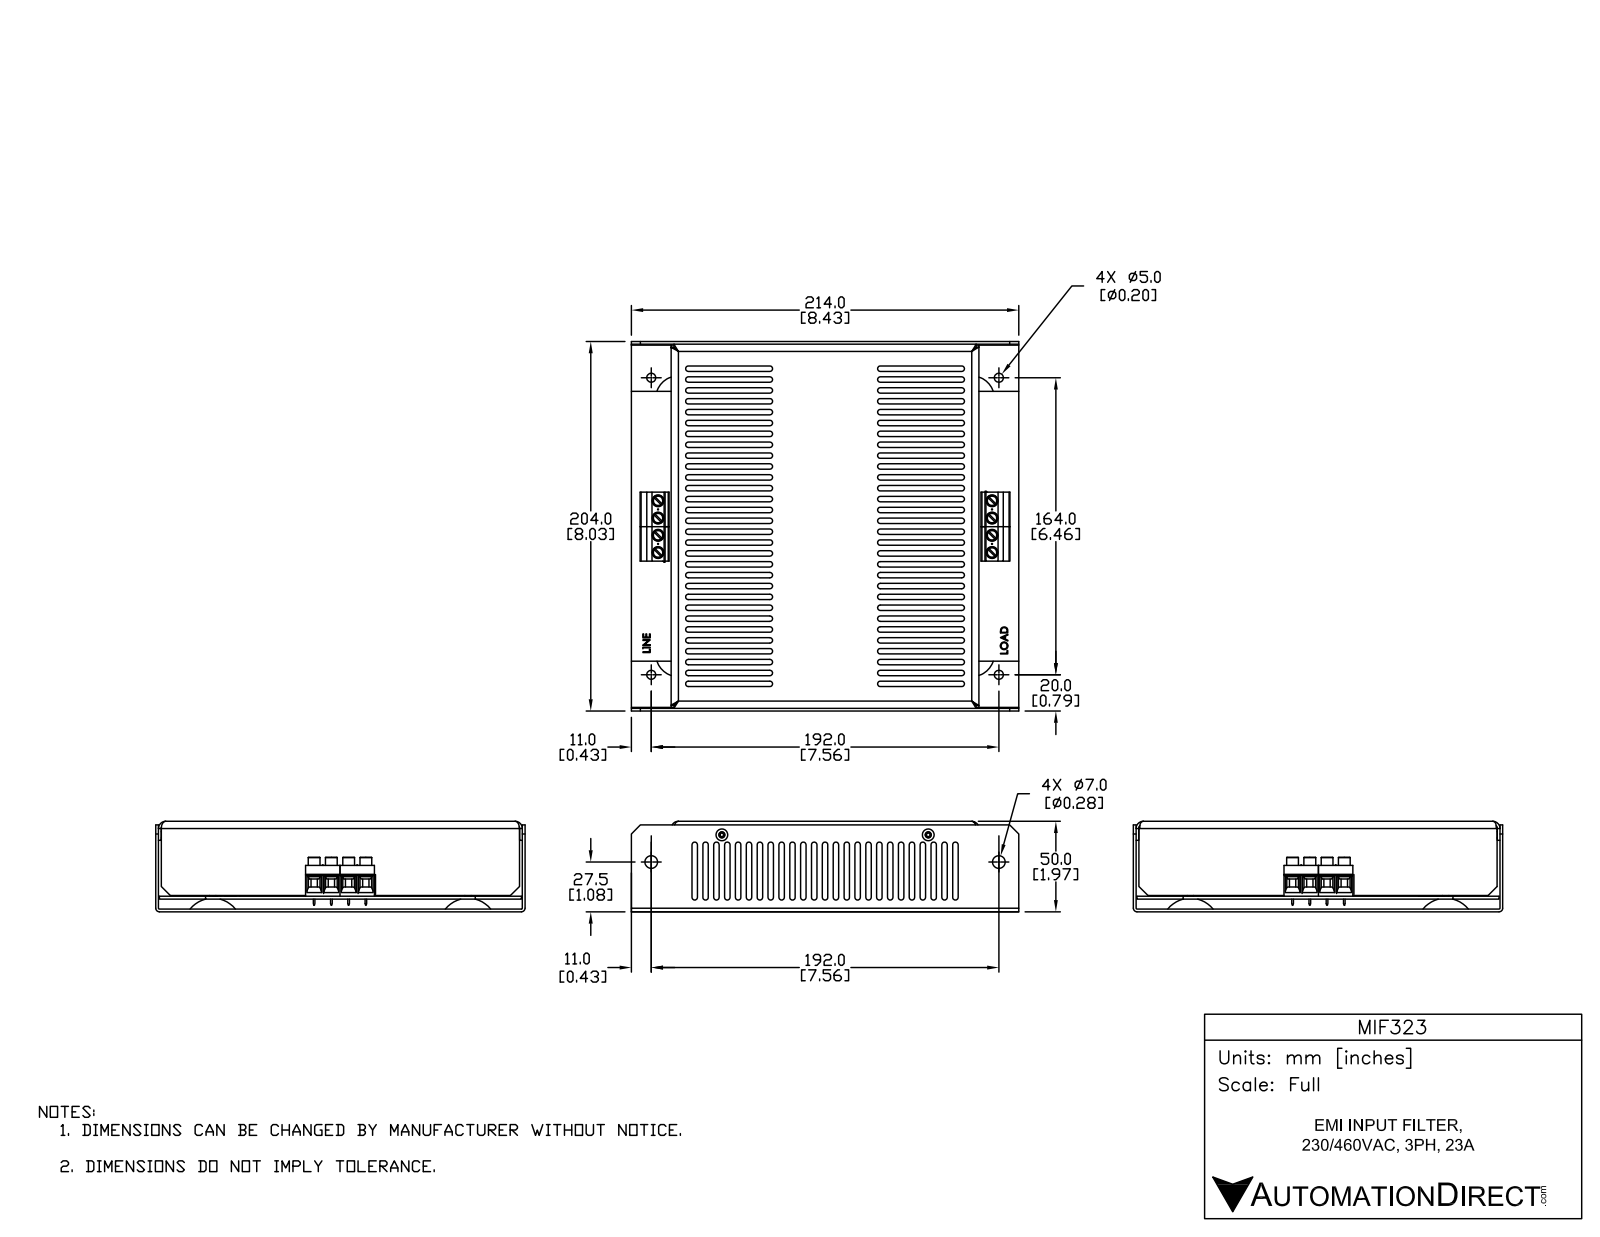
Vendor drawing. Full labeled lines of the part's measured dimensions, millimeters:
Part name (STEP PRODUCT): MIF316-323 new
STEP written by: SolidWorks 2017 (AUTOMOTIVE_DESIGN)
Units: millimetres
Bodies: 13 solids, 1317 faces (612 planar, 626 cylindrical, 79 other)
Overall size (bounding box): 214 × 204 × 50
Volume: 232 900 mm³ · Surface area: 313 600 mm²
Round holes (diameter × count): ⌀1.4 ×22, ⌀1.1 ×16, ⌀1.3 ×14, ⌀3.1 ×12, ⌀5 ×12, ⌀2 ×8, ⌀3.5 ×8, ⌀3 ×6, ⌀3.2 ×2, ⌀3.3 ×2, ⌀7 ×2
Round bosses / shafts (diameter × count): ⌀5.6 ×8, ⌀1.3 ×8, ⌀6.4 ×2, ⌀3.5 ×2
Partial cylindrical surfaces — rounded edges, fillets, slot ends (radius × count): R1.5 ×170, R0.5 ×6, R2.5 ×4, R4 ×4, R2 ×2
Main face-to-face distances: 1.5, 48.5, 8.6, 7.1, 5.5, 1.6, 7, 43, 50, 47
Hole centre spacings: 192, 18.9, 153.2, 177.4, 233.6, 14, 133.5, 30.8
